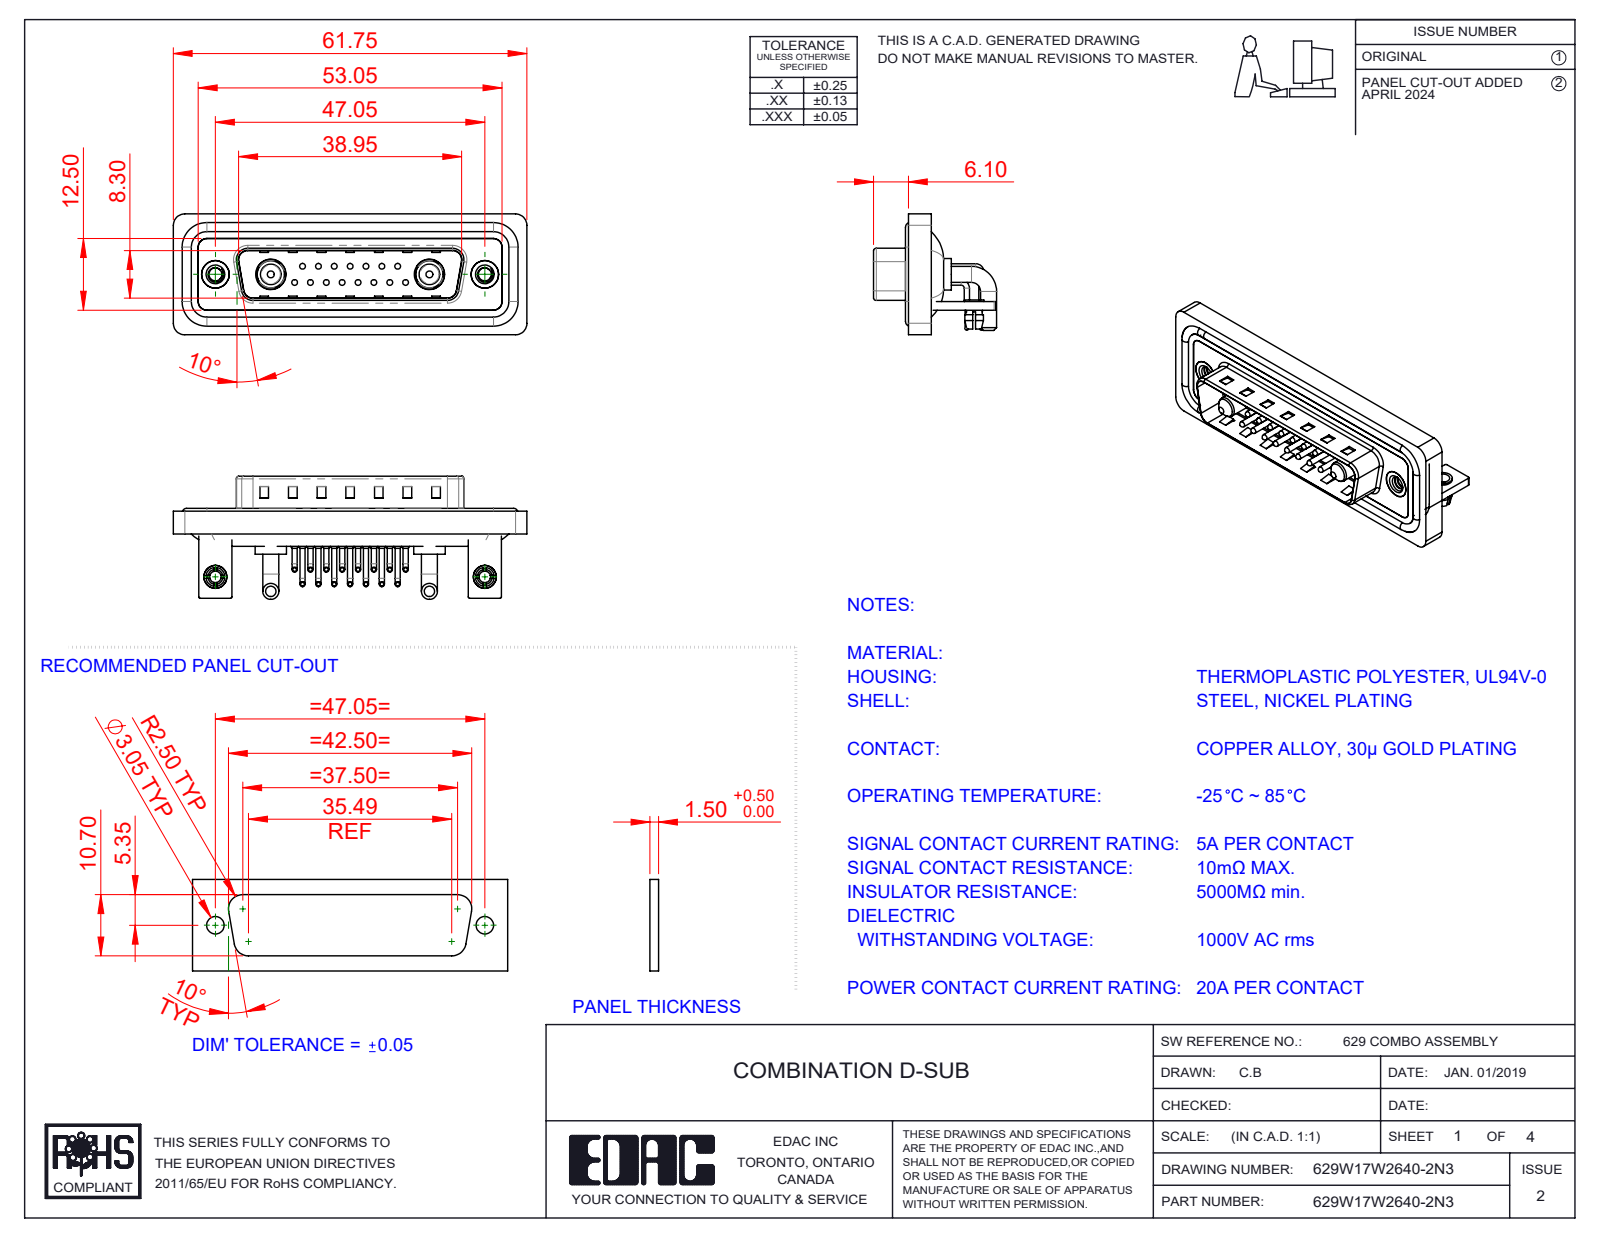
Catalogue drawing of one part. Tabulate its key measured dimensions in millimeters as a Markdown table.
| quantity | value |
| --- | --- |
| part name | 629Combo Threaded Rivet_3; 629Combo Waterproof Housing_25 Contacts; 629Combo Board Lock; 629Combo Contact Row 1 (+7 more) |
| STEP written by | SolidWorks 2023 (CONFIG_CONTROL_DESIGN) |
| units | millimeters |
| bodies | 30 solids, 2351 faces (1257 planar, 820 cylindrical, 274 other) |
| overall size | 61.75 × 21.5 × 21.1 |
| volume | 7 826 mm³ |
| surface area | 13 398 mm² |
| round holes (diameter × count) | 2 × 17, 0.75 × 15, 1.6 × 15, 2.26 × 2, 2.5 × 2, 3.2 × 2, 4 × 2, 4.8 × 2, 4.85 × 2, 5 × 2, 5.3 × 2 |
| round bosses / shafts (diameter × count) | 0.9 × 30, 1.5 × 15, 1 × 15, 0.65 × 15, 2.8 × 4, 1.6 × 4, 5.5 × 2, 5.2 × 2 |
| partial cylindrical surfaces (radius × count) | 2 × 19, 1.5 × 18, 0.25 × 16, 1.01 × 15, 0.5 × 9, 1.6 × 8, 0.6 × 4, 0.65 × 4 |
| main face-to-face distances | 0.4, 0.8, 1.5, 2.1, 2.9, 1.1, 4.1, 1.6, 4.5, 3.7 |
| hole center spacings | 3.16, 2.77, 5.54, 8.31, 5.04, 7.49, 11.08, 5.03 |
